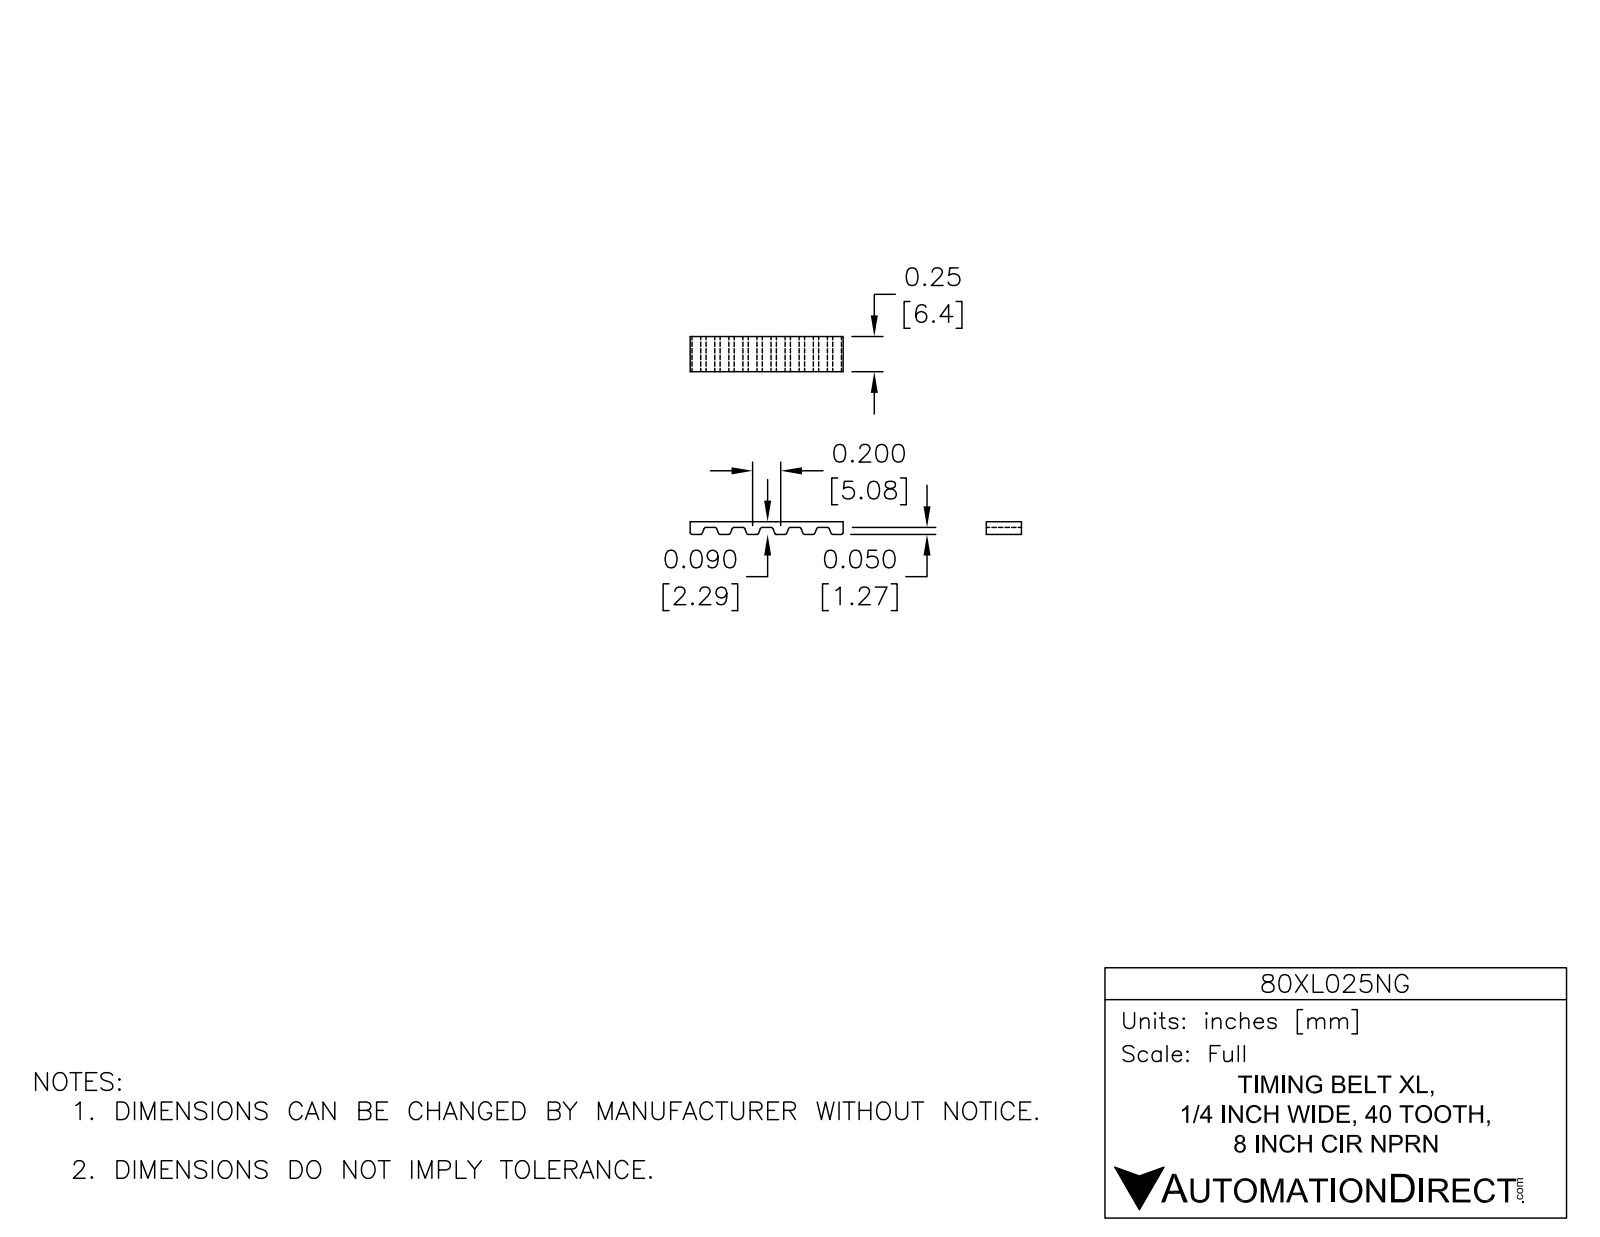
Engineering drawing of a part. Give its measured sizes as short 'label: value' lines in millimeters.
name: 80XL025NG
written by: SolidWorks 2014 (AUTOMOTIVE_DESIGN)
unit: mm
bodies: 1 solid, 349 faces (134 planar, 215 cylindrical, 0 other)
size: 72.6 × 50.8 × 6.4
volume: 1 770 mm³; area: 3 452 mm²
rounds: 160× R0.4, 2× R24.4, 2× R25.4
face distances: 6.4, 50.8, 1, 49.8, 48.8, 4.5, 8.9, 2.3, 48.5, 1.3
